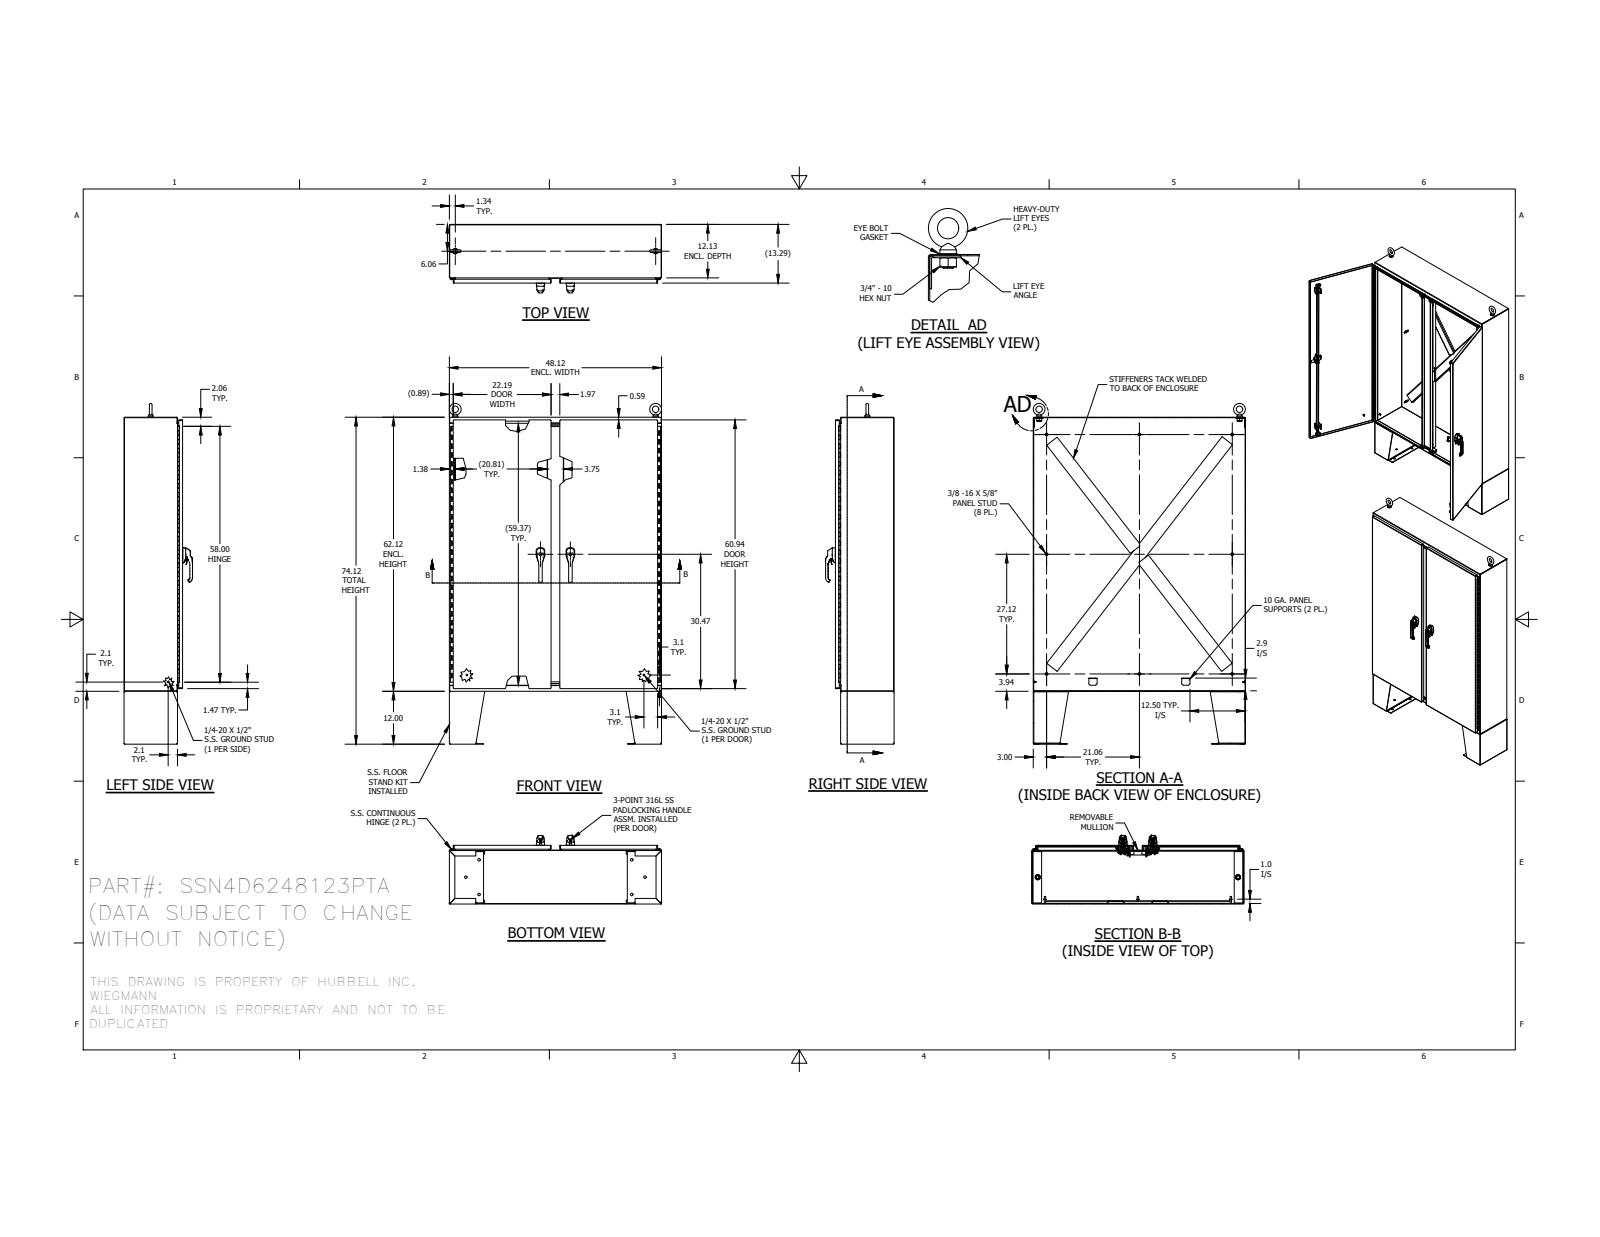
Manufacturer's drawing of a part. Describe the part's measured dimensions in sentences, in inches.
The part is named "328131P-58_1; 1225-05_1; 1091-74-01_1; SSN4D623PTRML_1 (+8 more)". Its 3-D file was written by "SolidWorks 2014 (AUTOMOTIVE_DESIGN)". It is 138 solids with 7184 faces: 2696 planar, 2772 cylindrical and 1716 other. Overall it measures 77.248 by 48.125 by 15.538 inches. Its volume is 1 161 cubic inches and its surface area 24 151 square inches. Round holes: 18 of diameter 0.563, 16 of diameter 0.262, 16 of diameter 0.375, 8 of diameter 0.187, 6 of diameter 0.213, 6 of diameter 0.281, 5 of diameter 0.25, 4 of diameter 0.196, 4 of diameter 0.241, 4 of diameter 0.252, 4 of diameter 0.281, 4 of diameter 0.315. Round bosses or shafts: 10 of diameter 0.33, 8 of diameter 0.625, 7 of diameter 0.25, 6 of diameter 0.533, 6 of diameter 0.236, 5 of diameter 1, 4 of diameter 0.563, 4 of diameter 0.531. Partial cylindrical surfaces (rounded edges, fillets, slot ends): 342 of radius 0.02, 213 of radius 0.012, 46 of radius 0.125, 42 of radius 0.019, 34 of radius 0.05, 32 of radius 0.031, 28 of radius 0.079, 24 of radius 0.025. The main face-to-face distances are 0.094, 13.196, 13.193, 48.031, 13.102, 13.1, 13.29, 0.096, 13.287, 0.091. The hole center spacings are 6.444, 0.38, 0.38, 0.76, 12.889, 46.321, 52.052, 52.427.
